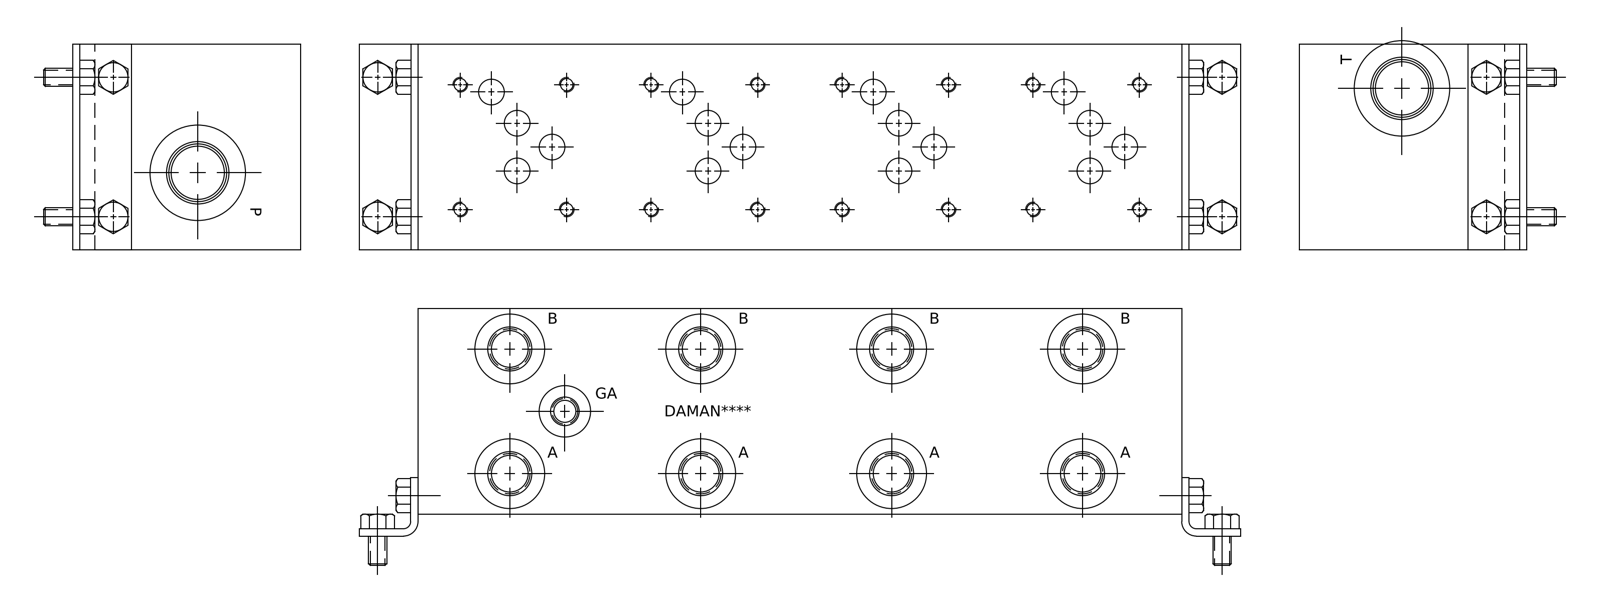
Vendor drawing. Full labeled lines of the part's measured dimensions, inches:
Part name (STEP PRODUCT): Part_AD05S043S.D02128R3_3D
STEP written by: Autodesk Inventor 2020 (AUTOMOTIVE_DESIGN)
Units: inches
Bodies: 1 solid, 776 faces (401 planar, 112 cylindrical, 263 other)
Overall size (bounding box): 13 × 3.5 × 3.5
Volume: 152.3 in³ · Surface area: 248.8 in²
Round holes (diameter × count): ⌀0.438 ×17, ⌀0.201 ×16, ⌀0.25 ×16, ⌀0.625 ×8, ⌀0.689 ×8, ⌀0.75 ×8, ⌀0.758 ×8, ⌀1.206 ×8, ⌀0.257 ×2, ⌀0.312 ×2, ⌀0.906 ×2, ⌀0.981 ×2
Main face-to-face distances: 3.5, 13, 0.031, 3.469, 12.969, 12.938, 0.562, 0.593, 2.907, 0.75
Hole centre spacings: 3.25, 6.5, 3.883, 0.719, 1.813, 2.687, 2.793, 3.883
